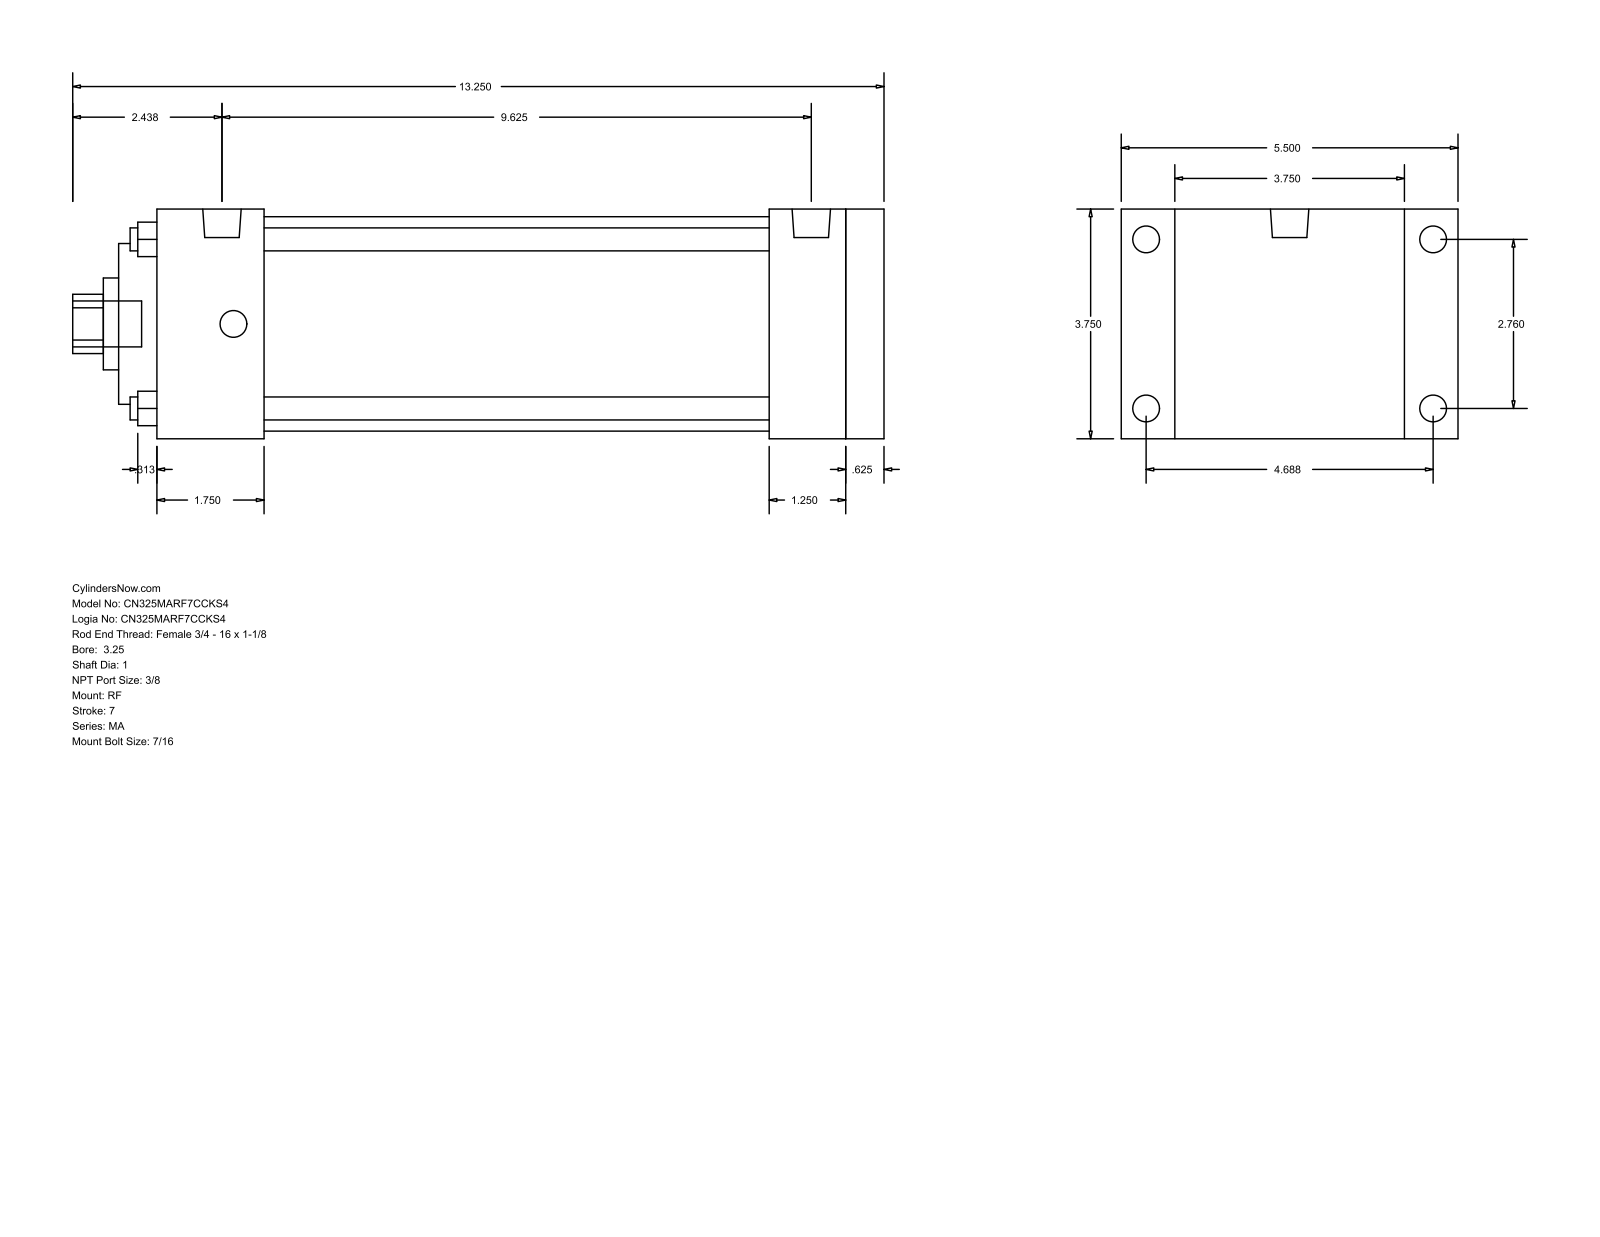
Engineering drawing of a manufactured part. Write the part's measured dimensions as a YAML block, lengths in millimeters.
part_name: "MA_RF__0325_1"
step_written_by: "GSSL Pune (CONFIG_CONTROL_DESIGN)"
units: millimeters
bodies: {solids: 0, faces: 94, planar: 65, cylindrical: 29, other: 0}
overall_size: [336.55, 139.7, 95.25]
round_holes:
  - {diameter: 9.53, count: 4}
  - {diameter: 25.4, count: 1}
  - {diameter: 38.1, count: 1}
  - {diameter: 66.67, count: 1}
  - {diameter: 88.9, count: 1}
round_bosses_or_shafts:
  - {diameter: 11.11, count: 8}
  - {diameter: 15.93, count: 2}
  - {diameter: 19.05, count: 1}
partial_cylinders:
  - {radius: 12.29, count: 1}
face_to_face_distances: [95.24, 301.63, 15.87, 285.76, 22.23, 117.47, 254.01, 31.75, 47.62, 44.46]
hole_center_spacings: [49.57, 70.1, 99.14]
